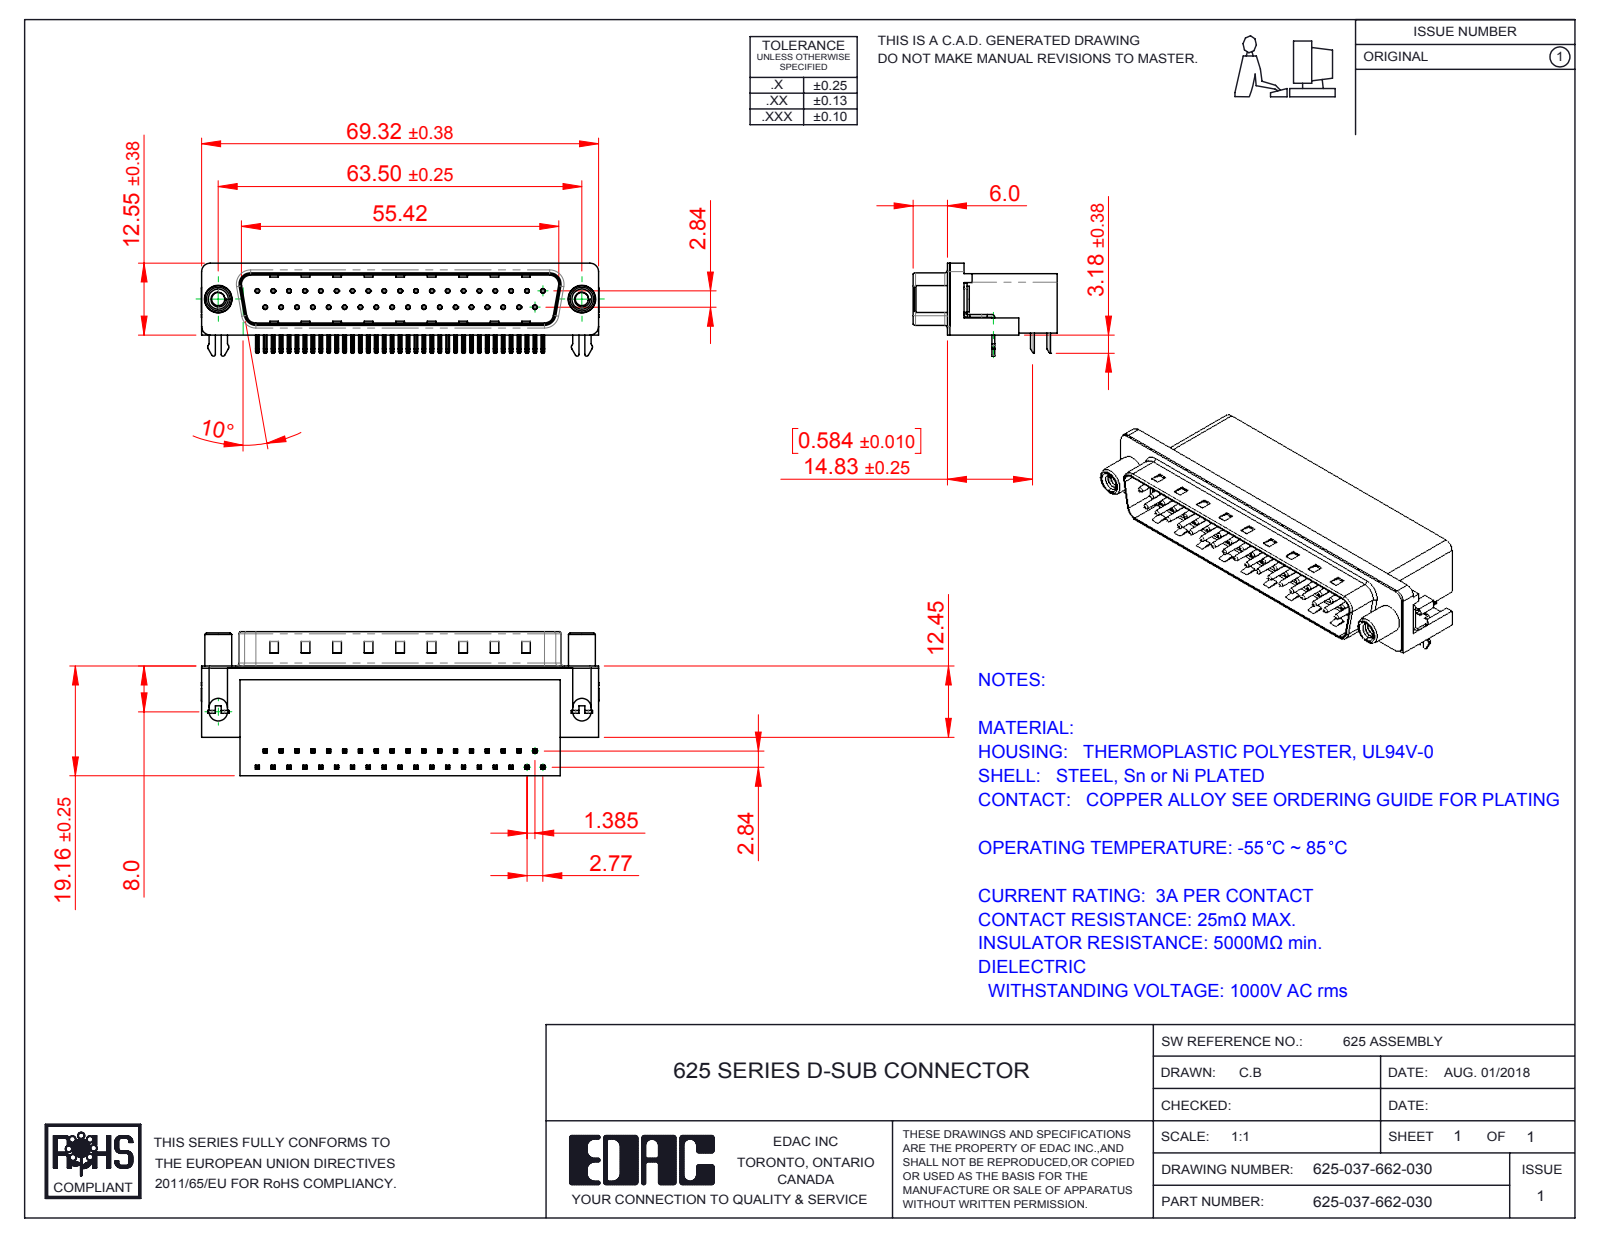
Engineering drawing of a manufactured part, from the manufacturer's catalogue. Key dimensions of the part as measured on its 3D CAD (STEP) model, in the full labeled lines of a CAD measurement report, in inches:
Part name (STEP PRODUCT): 625 Round Threaded Standoff; 625-037-662-030; 625 Housing_37 Socket; 625 Contact Top (+3 more)
STEP written by: SolidWorks 2016 (CONFIG_CONTROL_DESIGN)
Units: inches
Bodies: 43 solids, 3235 faces (2037 planar, 933 cylindrical, 265 other)
Overall size (bounding box): 2.732 × 0.991 × 0.64
Volume: 0.774 in³ · Surface area: 18.54 in²
Round holes (diameter × count): ⌀0.014 ×37, ⌀0.031 ×37, ⌀0.091 ×2, ⌀0.122 ×2, ⌀0.157 ×2, ⌀0.189 ×2, ⌀0.197 ×2
Round bosses / shafts (diameter × count): ⌀0.03 ×37, ⌀0.193 ×2, ⌀0.185 ×2, ⌀0.177 ×2, ⌀0.152 ×2
Partial cylindrical surfaces — rounded edges, fillets, slot ends (radius × count): R0.01 ×148, R0.005 ×74, R0.039 ×16, R0.02 ×14, R0.063 ×8, R0.059 ×7, R0.013 ×4, R0.035 ×4
Main face-to-face distances: 0.407, 0.016, 0.739, 0.345, 0.112, 0.754, 0.082, 0.398, 0.069, 0.329
Hole centre spacings: 0.124, 0.109, 0.218, 0.327, 0.436, 0.545, 0.763, 0.872
